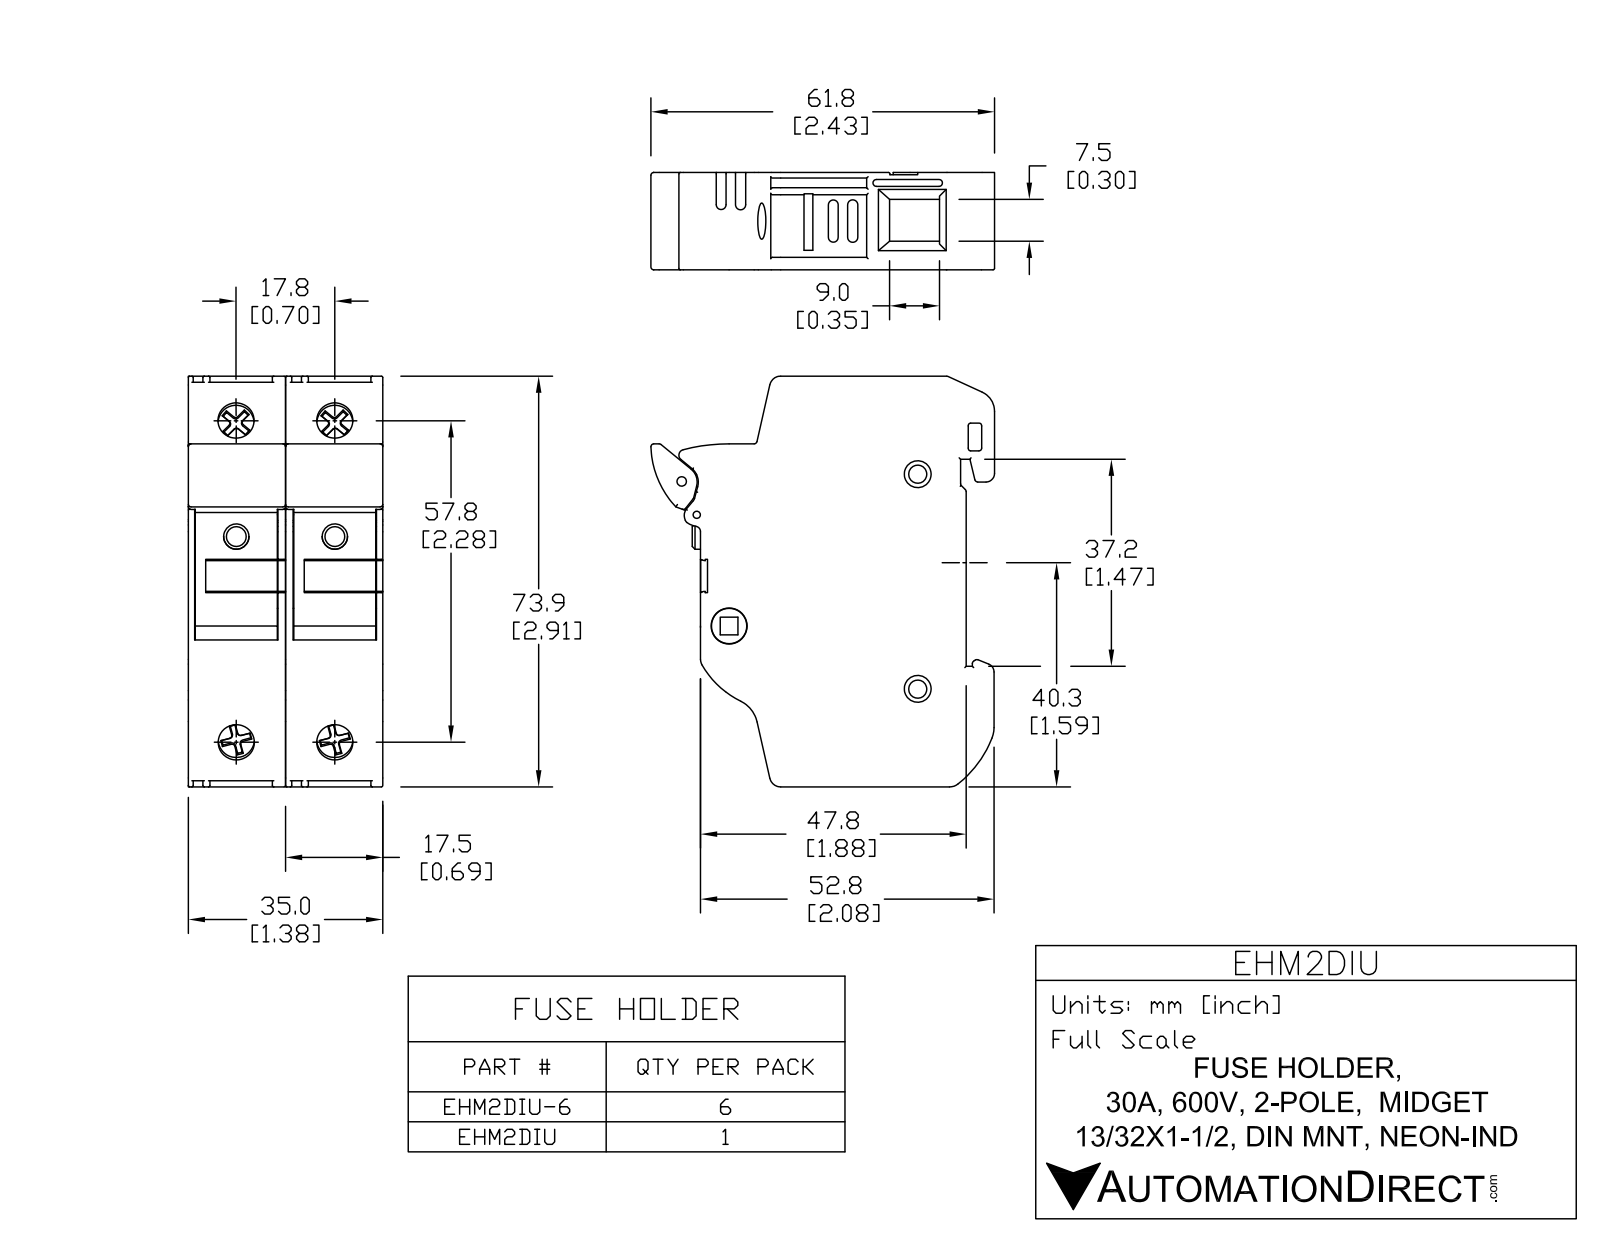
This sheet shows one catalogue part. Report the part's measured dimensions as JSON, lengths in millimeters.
{"part_name": "EHM2DIU", "step_written_by": "SolidWorks 2017 (AUTOMOTIVE_DESIGN)", "units": "millimeters", "bodies": {"solids": 4, "faces": 1178, "planar": 494, "cylindrical": 392, "other": 292}, "overall_size": [73.88, 61.82, 35], "volume_mm3": 105488, "surface_area_mm2": 39190, "round_holes": [[6.5, 4], [3.25, 2], [4.83, 2], [1.3, 1], [1.7, 1], [6.48, 1]], "round_bosses_or_shafts": [[4.55, 2], [6.35, 1]], "partial_cylinders_radius": [[0.25, 134], [0.5, 11], [2, 10], [0.51, 9], [0.62, 8], [1, 7], [0.89, 6], [0.92, 6]], "face_to_face_distances": [17.5, 35, 1.25, 1.58, 16.25, 27.51, 29.09, 22.94, 24.71, 0.4], "hole_center_spacings": [17.5, 6.58, 20.83, 27.36, 35.77, 35.79, 38.61, 38.66]}
